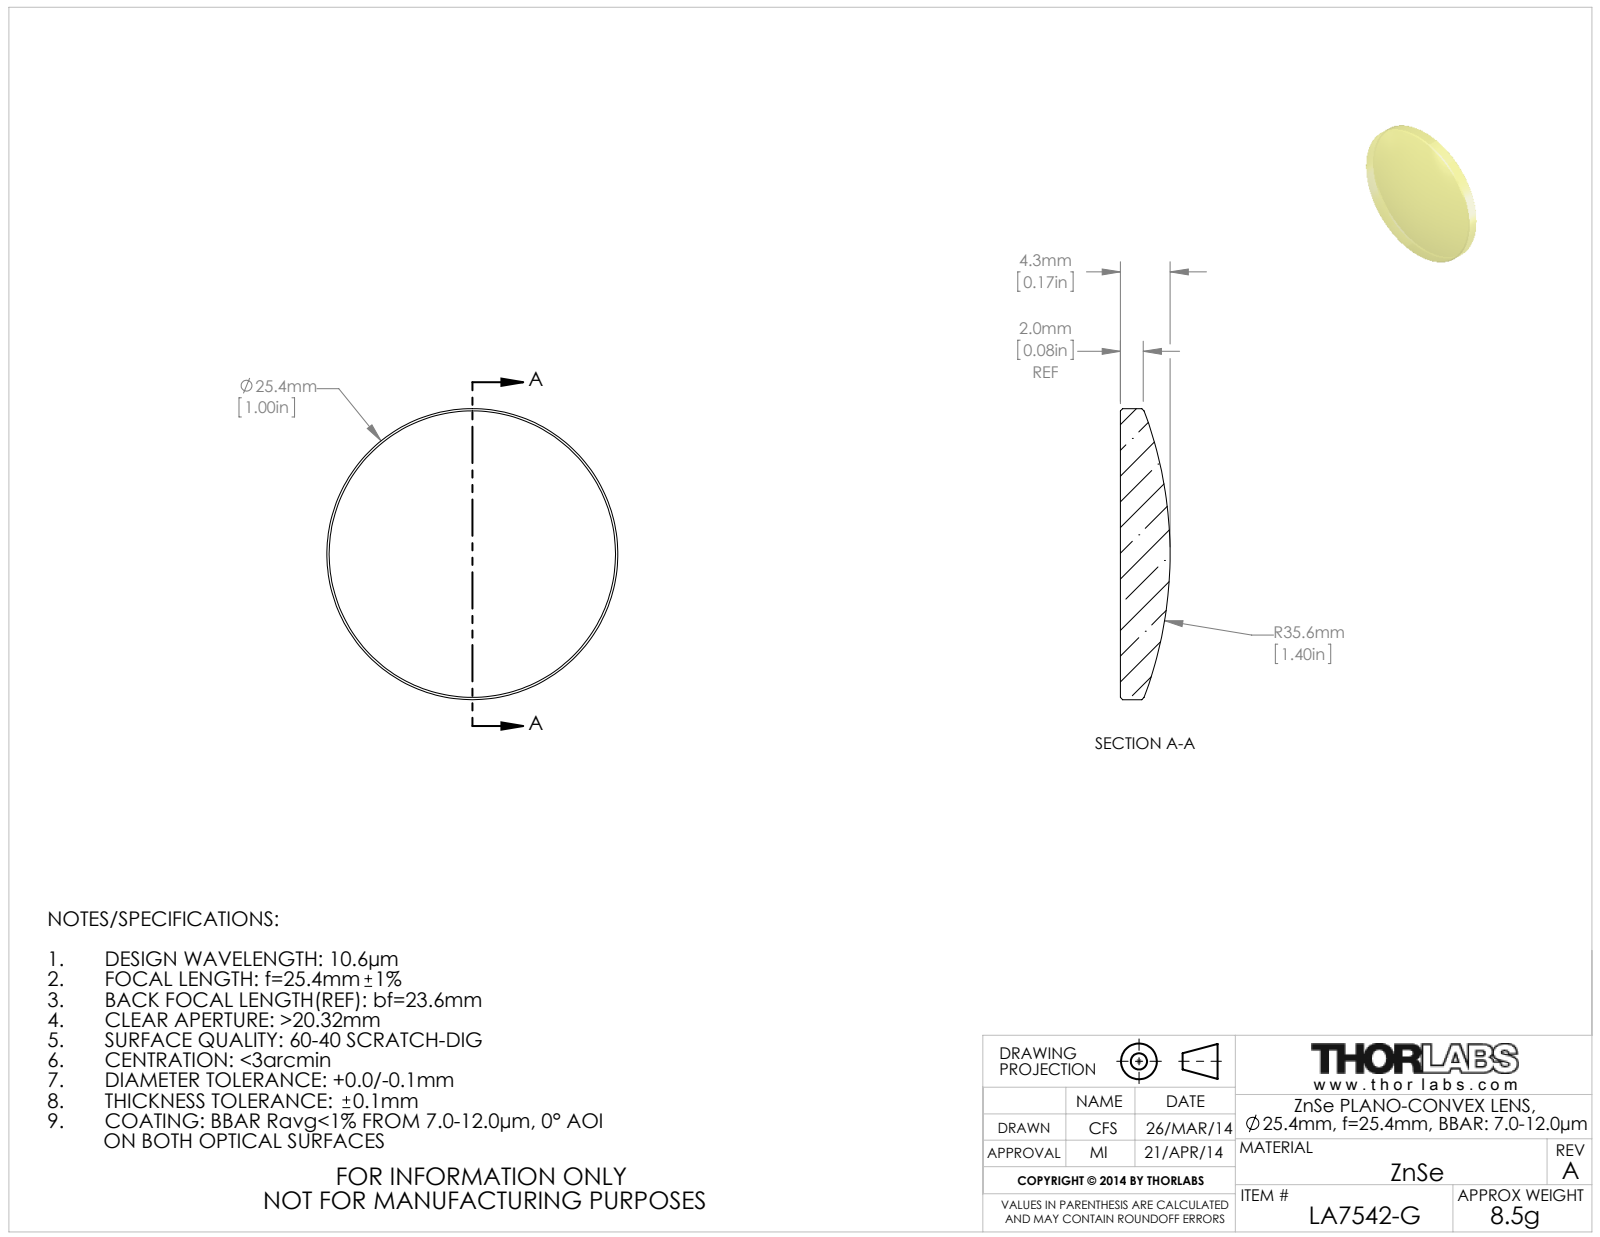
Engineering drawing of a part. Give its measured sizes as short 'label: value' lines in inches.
name: TTN023912-E0W
written by: SolidWorks 2012 (CONFIG_CONTROL_DESIGN)
unit: in
bodies: 1 solid, 9 faces (1 planar, 2 cylindrical, 6 other)
size: 1 × 1 × 0.171
volume: 0.098 in³; area: 1.823 in²
bosses: 1× ⌀1
